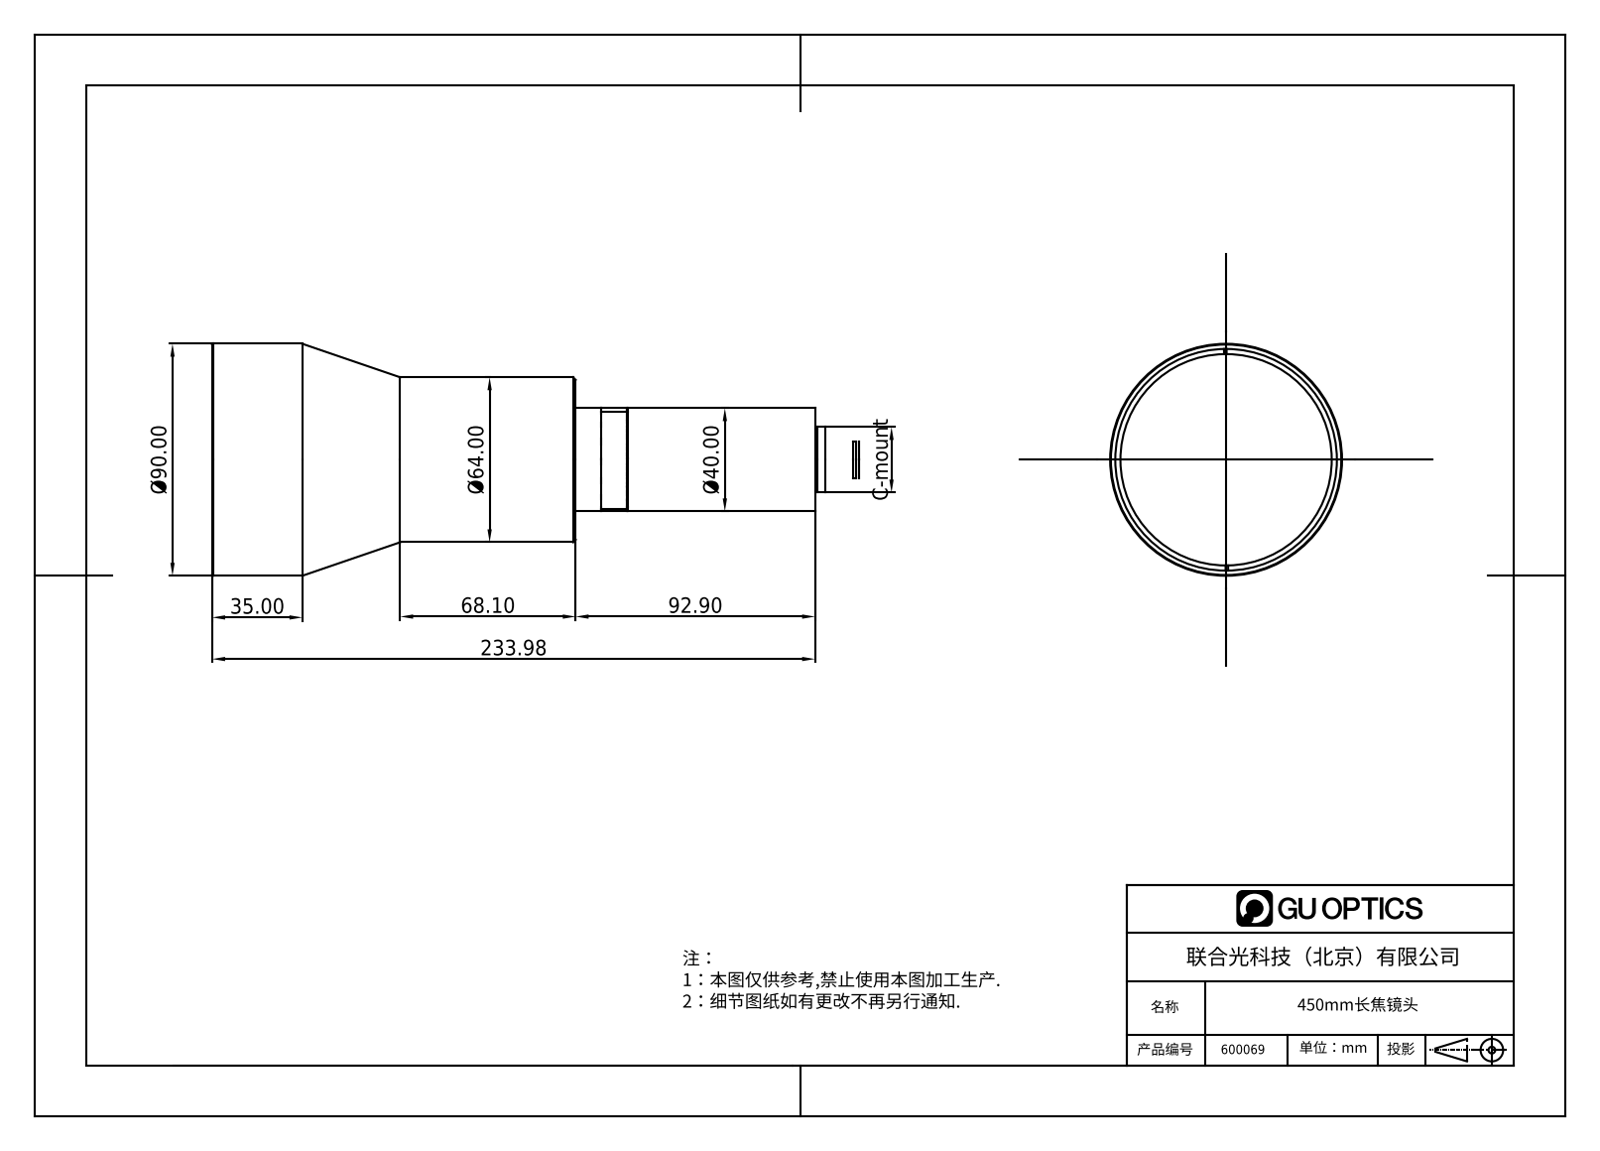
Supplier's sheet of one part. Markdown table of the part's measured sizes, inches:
| quantity | value |
| --- | --- |
| part name | 600069 |
| STEP written by | SolidWorks 2020 (CONFIG_CONTROL_DESIGN) |
| units | inches |
| bodies | 18 solids, 269 faces (88 planar, 154 cylindrical, 27 other) |
| overall size | 9.878 × 3.543 × 3.543 |
| volume | 21 in³ |
| surface area | 256.4 in² |
| round holes (diameter × count) | 0.063 × 2, 3.228 × 2, 0.049 × 1, 0.843 × 1, 0.866 × 1, 0.906 × 1, 0.984 × 1, 1.063 × 1, 1.087 × 1, 1.142 × 1, 1.26 × 1, 1.339 × 1 |
| round bosses / shafts (diameter × count) | 3.543 × 1, 3.386 × 1, 3.307 × 1, 2.937 × 1, 2.52 × 1, 2.244 × 1, 1.575 × 1, 1.457 × 1 |
| partial cylindrical surfaces (radius × count) | 0.079 × 64, 0.059 × 2, 0.768 × 1 |
| main face-to-face distances | 0.118, 5.062, 5.18, 1.913, 0.374, 3.15, 3.268, 3.657, 1.539, 3.524 |
